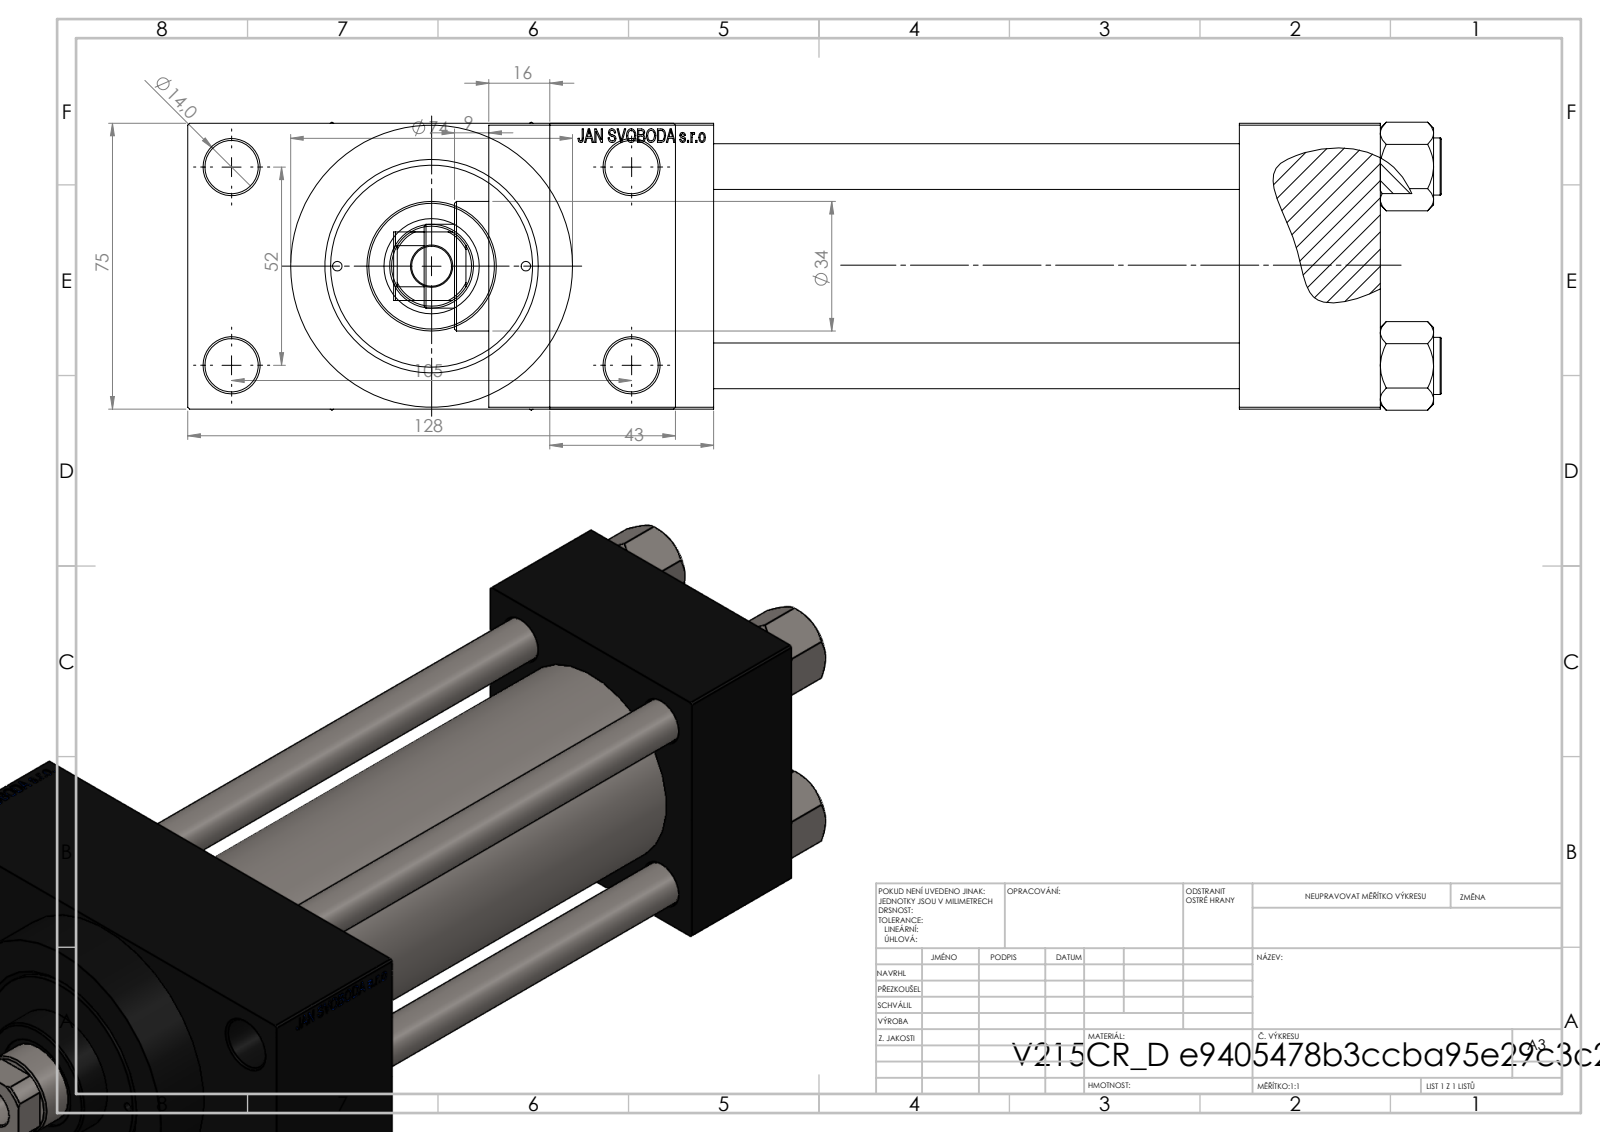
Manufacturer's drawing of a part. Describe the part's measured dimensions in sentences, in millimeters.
The part is named "V215CR_VCP_D; NUT_M5_D; V215_VC_A; V215CR_D_TYCINKA (+1 more)". Its 3-D file was written by "SolidWorks 2019 (CONFIG_CONTROL_DESIGN)". It is 11 solids with 1111 faces: 499 planar, 92 cylindrical and 520 other. Overall it measures 275 by 128 by 75.54 millimeters. Its volume is 903 841 cubic millimeters and its surface area 210 856 square millimeters. Round holes: 4 of diameter 12, 4 of diameter 14, 2 of diameter 2.5, 2 of diameter 7, 2 of diameter 20.96, 2 of diameter 30, 1 of diameter 10.5, 1 of diameter 22, 1 of diameter 25, 1 of diameter 41, 1 of diameter 50, 1 of diameter 53. Round bosses or shafts: 4 of diameter 15, 1 of diameter 74, 1 of diameter 56, 1 of diameter 34. Partial cylindrical surfaces (rounded edges, fillets, slot ends): 1 of radius 10.5. The main face-to-face distances are 75, 138, 37, 175, 26.5, 218, 181, 43, 101.5, 16. The hole center spacings are 26.19, 26.35, 36.98, 38.03, 52.3, 57.22, 58.43, 58.59.
